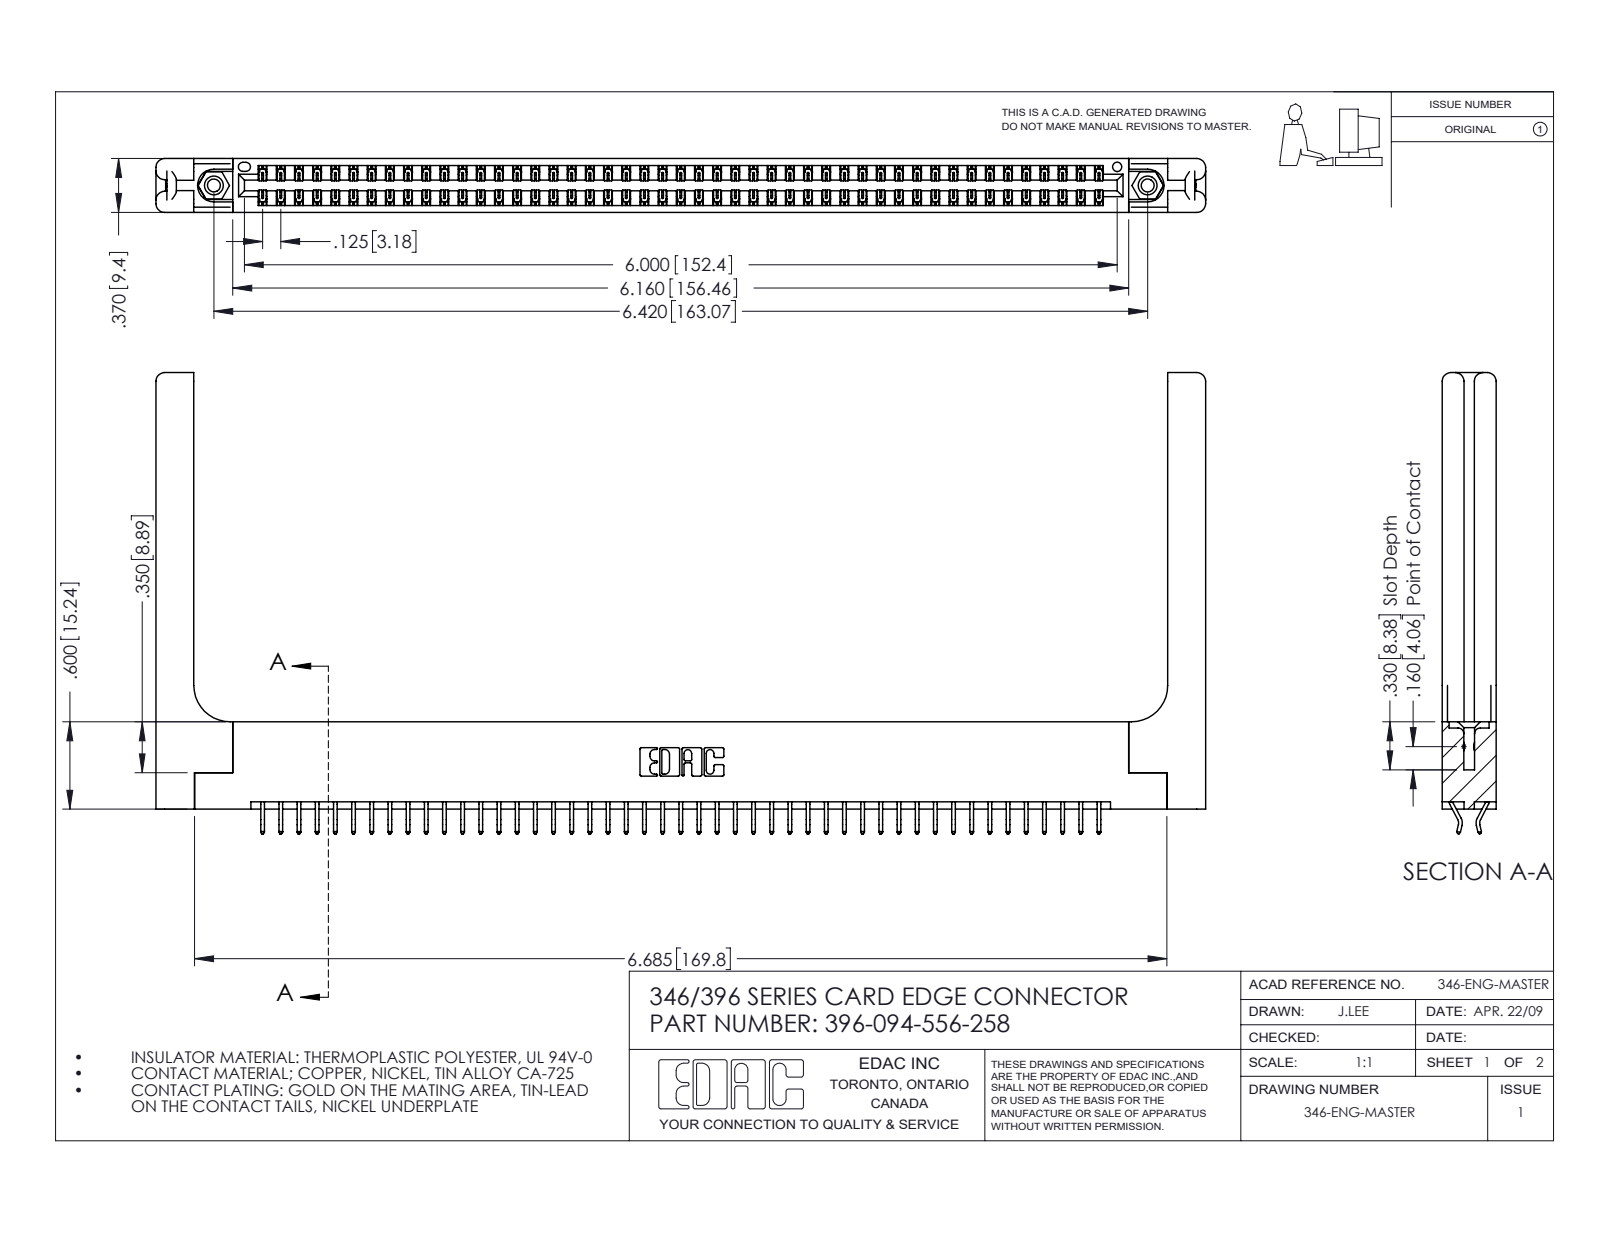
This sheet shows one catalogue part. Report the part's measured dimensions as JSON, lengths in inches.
{"part_name": "345-292-001_556 Tail; 346-220-058_345-220-058; 346 Part_Flush Mounting Lugs - 0.156 Dia-TH; 345-250-001_345-250-001-102 (+1 more)", "step_written_by": "SolidWorks 2016 (CONFIG_CONTROL_DESIGN)", "units": "inches", "bodies": {"solids": 99, "faces": 5830, "planar": 3890, "cylindrical": 1880, "other": 60}, "overall_size": [7.216, 3.17, 0.37], "volume_in3": 1.55, "surface_area_in2": 45.85, "round_holes": [[0.089, 2], [0.125, 2], [0.156, 2], [0.064, 1]], "round_bosses_or_shafts": [[0.155, 2]], "partial_cylinders_radius": [[0.006, 141], [0.01, 22], [0.06, 16], [0.007, 6], [0.031, 6], [0.026, 3], [0.01, 2], [0.014, 2]], "face_to_face_distances": [0.37, 0.048, 0.322, 0.072, 0.148, 0.15, 0.25, 0.025, 0.298, 0.275], "hole_center_spacings": [0.246, 6.211, 6.42]}
